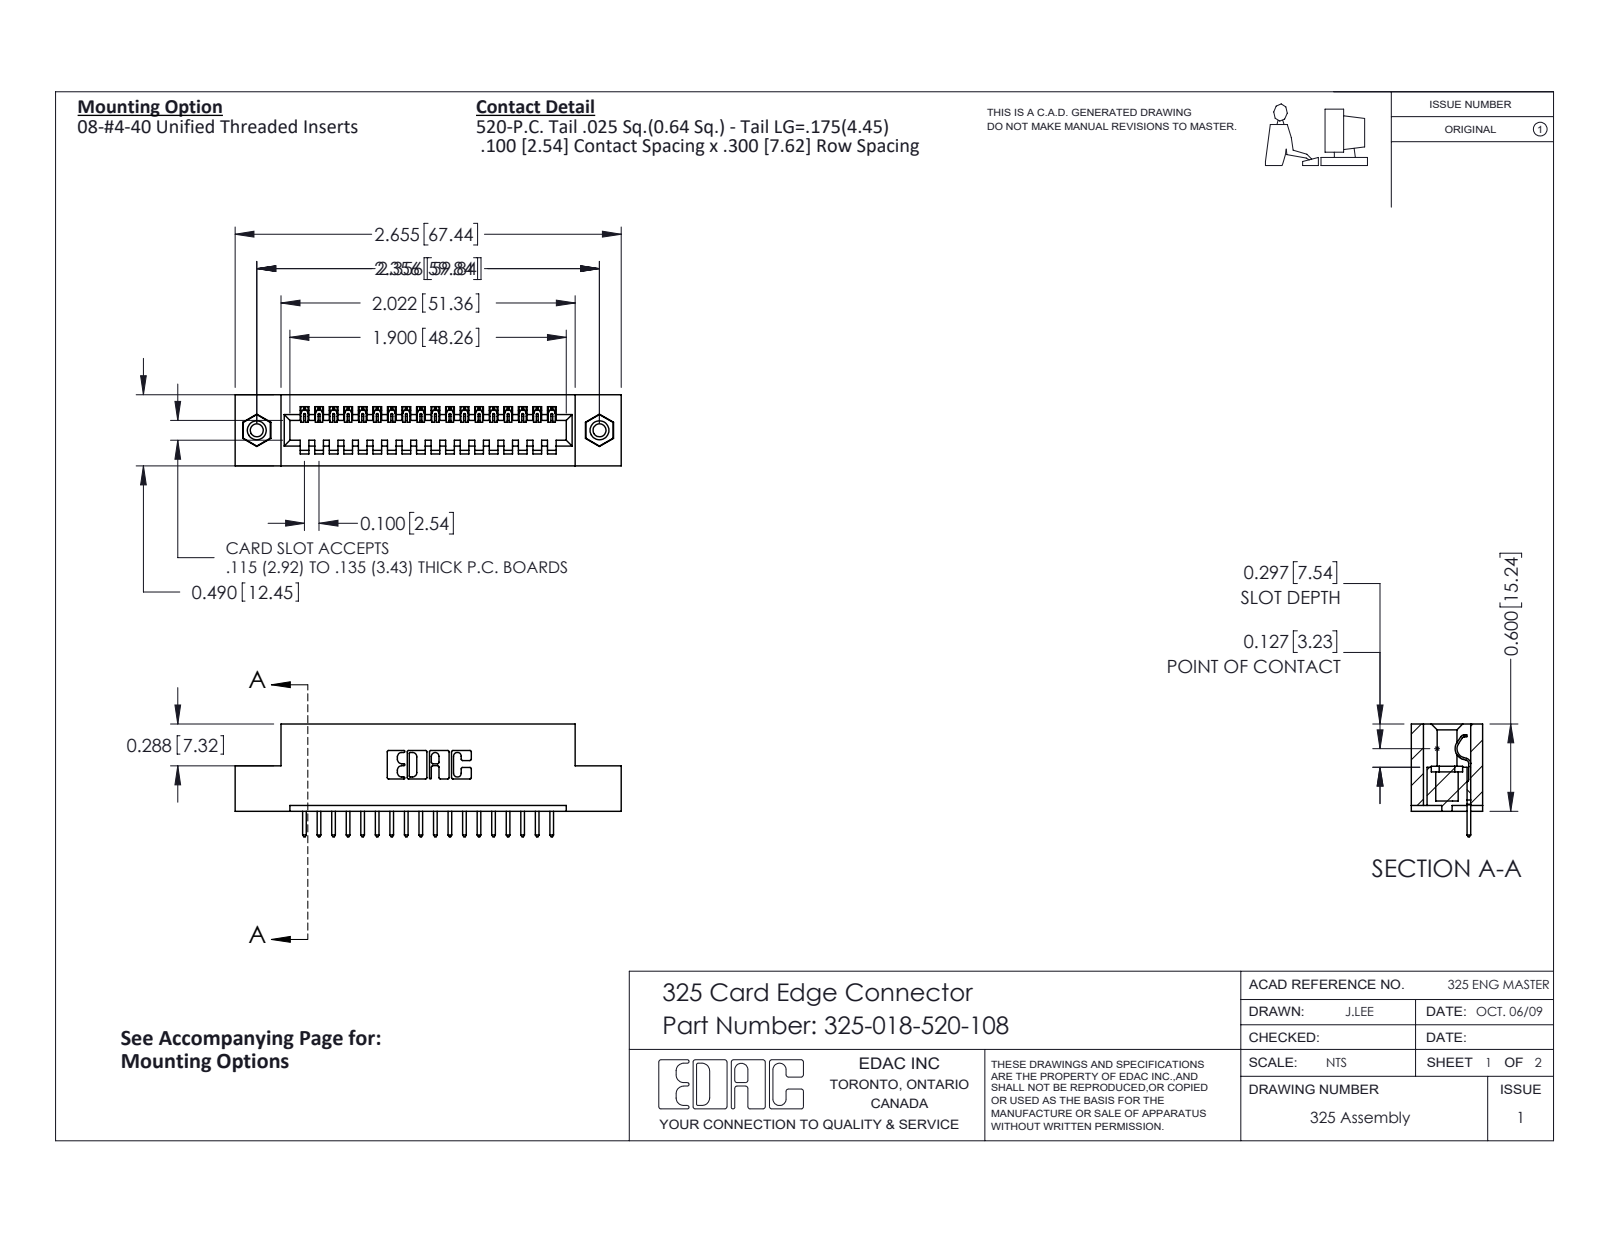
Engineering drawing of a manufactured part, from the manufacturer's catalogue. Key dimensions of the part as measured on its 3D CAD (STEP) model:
Part name (STEP PRODUCT): 325-018-520-108; 345-250-001_345-250-003-102; 325-292-001_325-293-120; 325 Part_TI
STEP written by: SolidWorks 2016 (CONFIG_CONTROL_DESIGN)
Units: inches
Bodies: 21 solids, 1218 faces (858 planar, 344 cylindrical, 16 other)
Overall size (bounding box): 2.655 × 0.775 × 0.49
Volume: 0.508 in³ · Surface area: 13.19 in²
Round holes (diameter × count): ⌀0.089 ×2, ⌀0.125 ×2, ⌀0.16 ×2
Round bosses / shafts (diameter × count): ⌀0.155 ×2
Partial cylindrical surfaces — rounded edges, fillets, slot ends (radius × count): R0.006 ×36, R0.01 ×36, R0.01 ×22, R0.007 ×6, R0.031 ×6, R0.026 ×3, R0.014 ×1, R0.022 ×1
Main face-to-face distances: 0.083, 0.407, 0.49, 0.3, 0.6, 0.107, 0.383, 0.025, 0.2, 0.04
Hole centre spacings: 2.356
